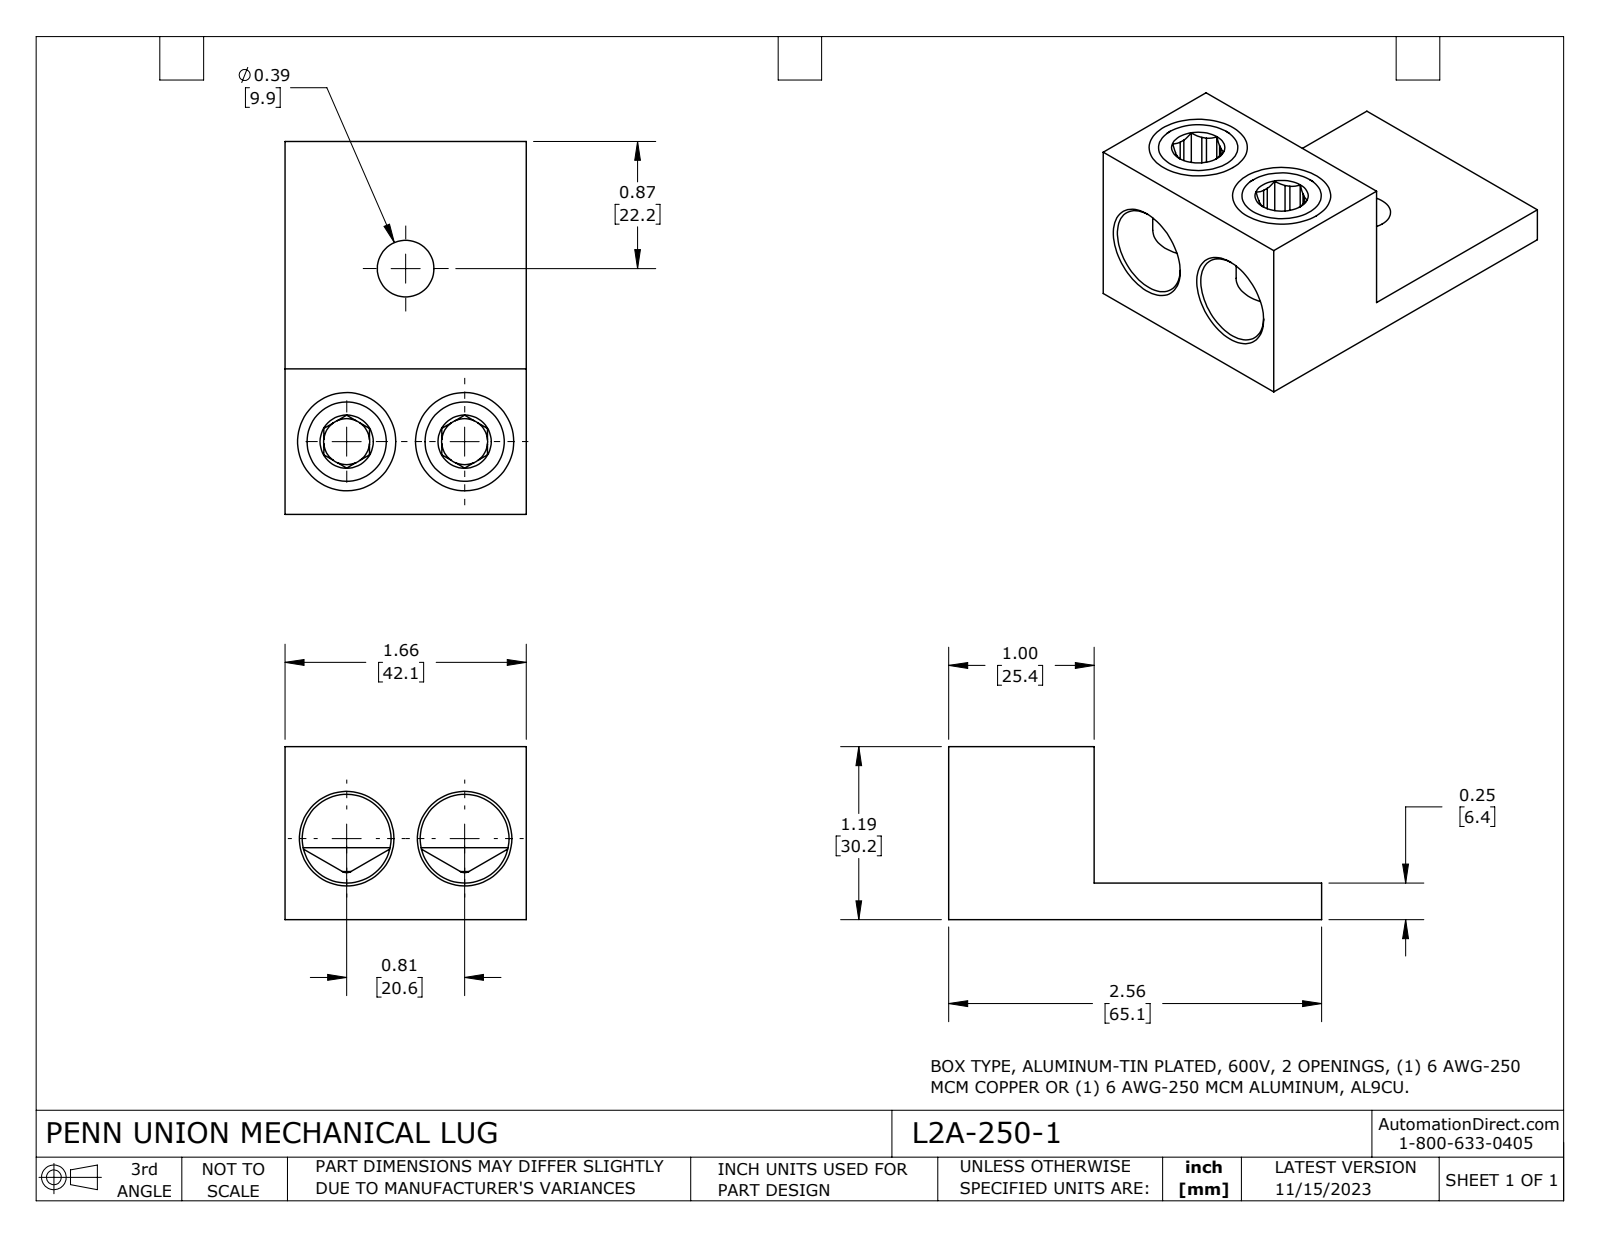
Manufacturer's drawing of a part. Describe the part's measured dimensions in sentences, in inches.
The part is named "L2A-250-1". Its 3-D file was written by "SolidWorks 2023 (CONFIG_CONTROL_DESIGN)". It is 3 solids with 90 faces: 46 planar, 18 cylindrical and 26 other. Overall it measures 2.563 by 1.657 by 1.189 inches. Its volume is 2.167 cubic inches and its surface area 23.76 square inches. Round holes: 2 of diameter 0.316, 2 of diameter 0.578, 2 of diameter 0.61, 1 of diameter 0.39. Round bosses or shafts: 2 of diameter 0.625. The main face-to-face distances are 0.252, 1.657, 1.189, 0.937, 1, 0.314, 2.563, 1.563, 0.406, 0.266. The hole center spacings are 0.811, 1.256.
